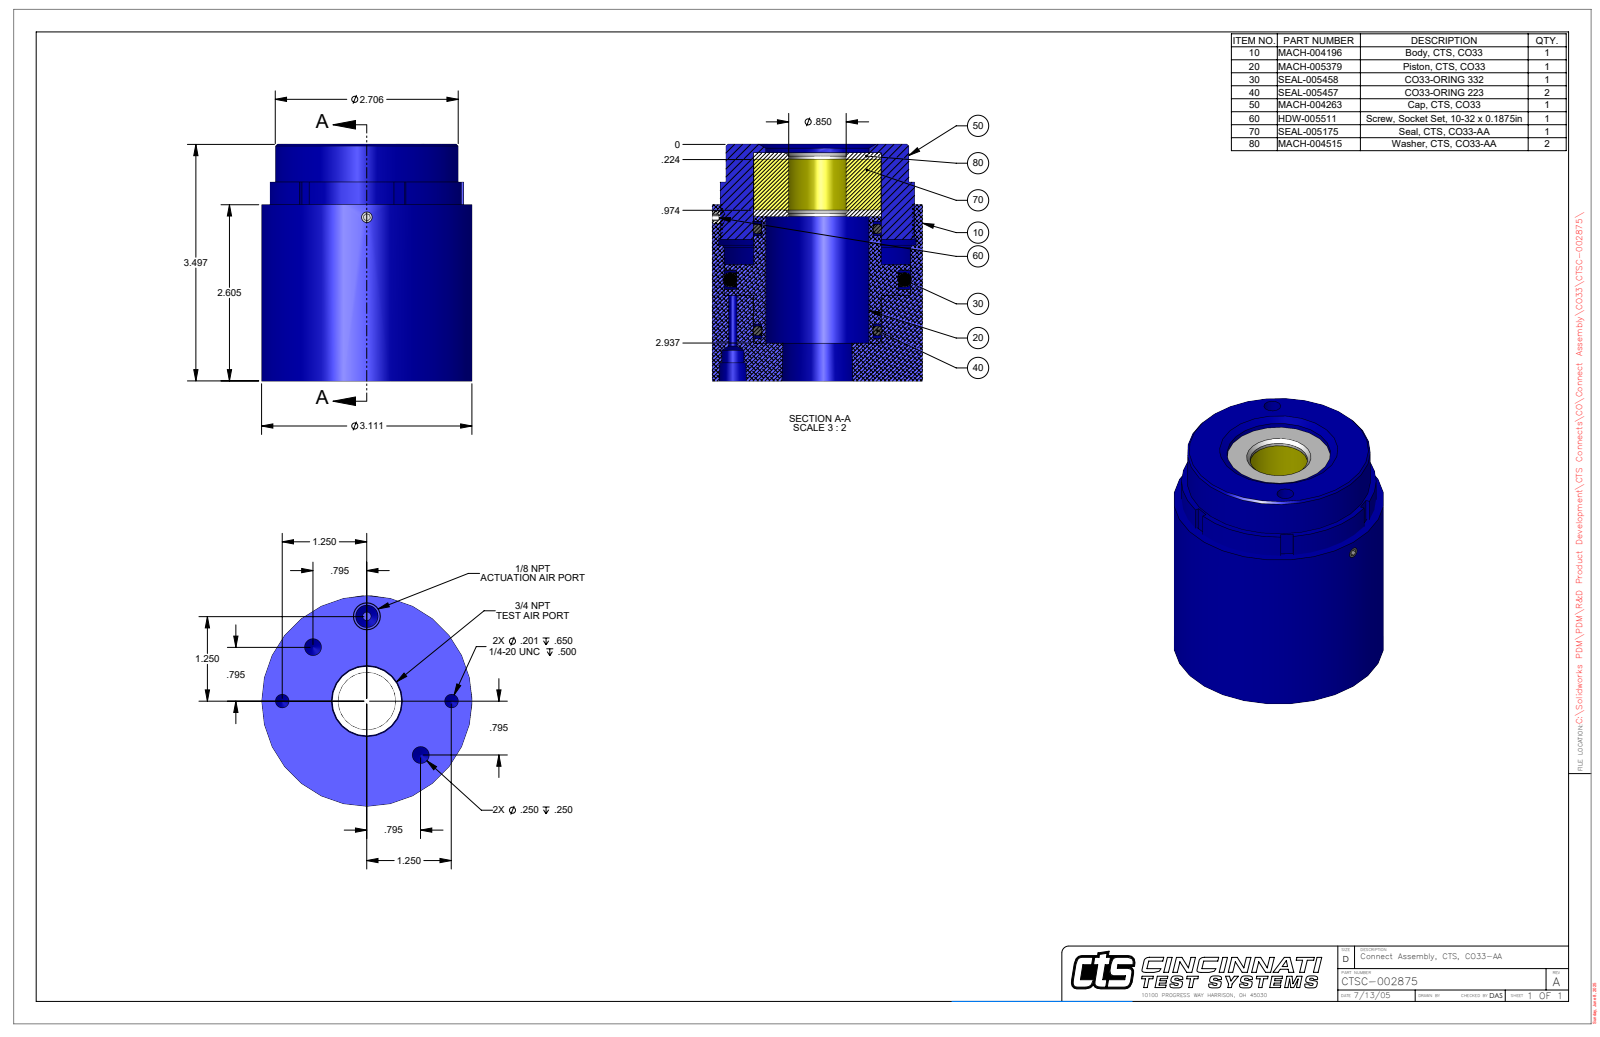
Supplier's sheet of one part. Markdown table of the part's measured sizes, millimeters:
| quantity | value |
| --- | --- |
| part name | CTSC-002875 |
| STEP written by | SolidWorks 2023 (AUTOMOTIVE_DESIGN) |
| units | millimeters |
| bodies | 1 solid, 122 faces (49 planar, 53 cylindrical, 20 other) |
| overall size | 88.8 × 79 × 79 |
| volume | 332 800 mm³ |
| surface area | 42 990 mm² |
| round holes (diameter × count) | 6.4 × 4, 5.1 × 2, 2.4 × 1, 3.2 × 1, 4 × 1, 8.4 × 1, 21.6 × 1, 21.6 × 1, 38.8 × 1, 38.8 × 1, 48.1 × 1 |
| round bosses / shafts (diameter × count) | 79 × 1, 73 × 1, 68.7 × 1, 47.9 × 1 |
| partial cylindrical surfaces (radius × count) | 35.7 × 1, 38.3 × 1 |
| main face-to-face distances | 88.8, 14.2, 74.6, 61.7, 27.1, 85.5, 23.8, 3.3, 66.2, 4.5 |
| hole center spacings | 28.6, 23.3, 31.8, 55.8, 2.4, 25.6, 44.9, 54.7 |
